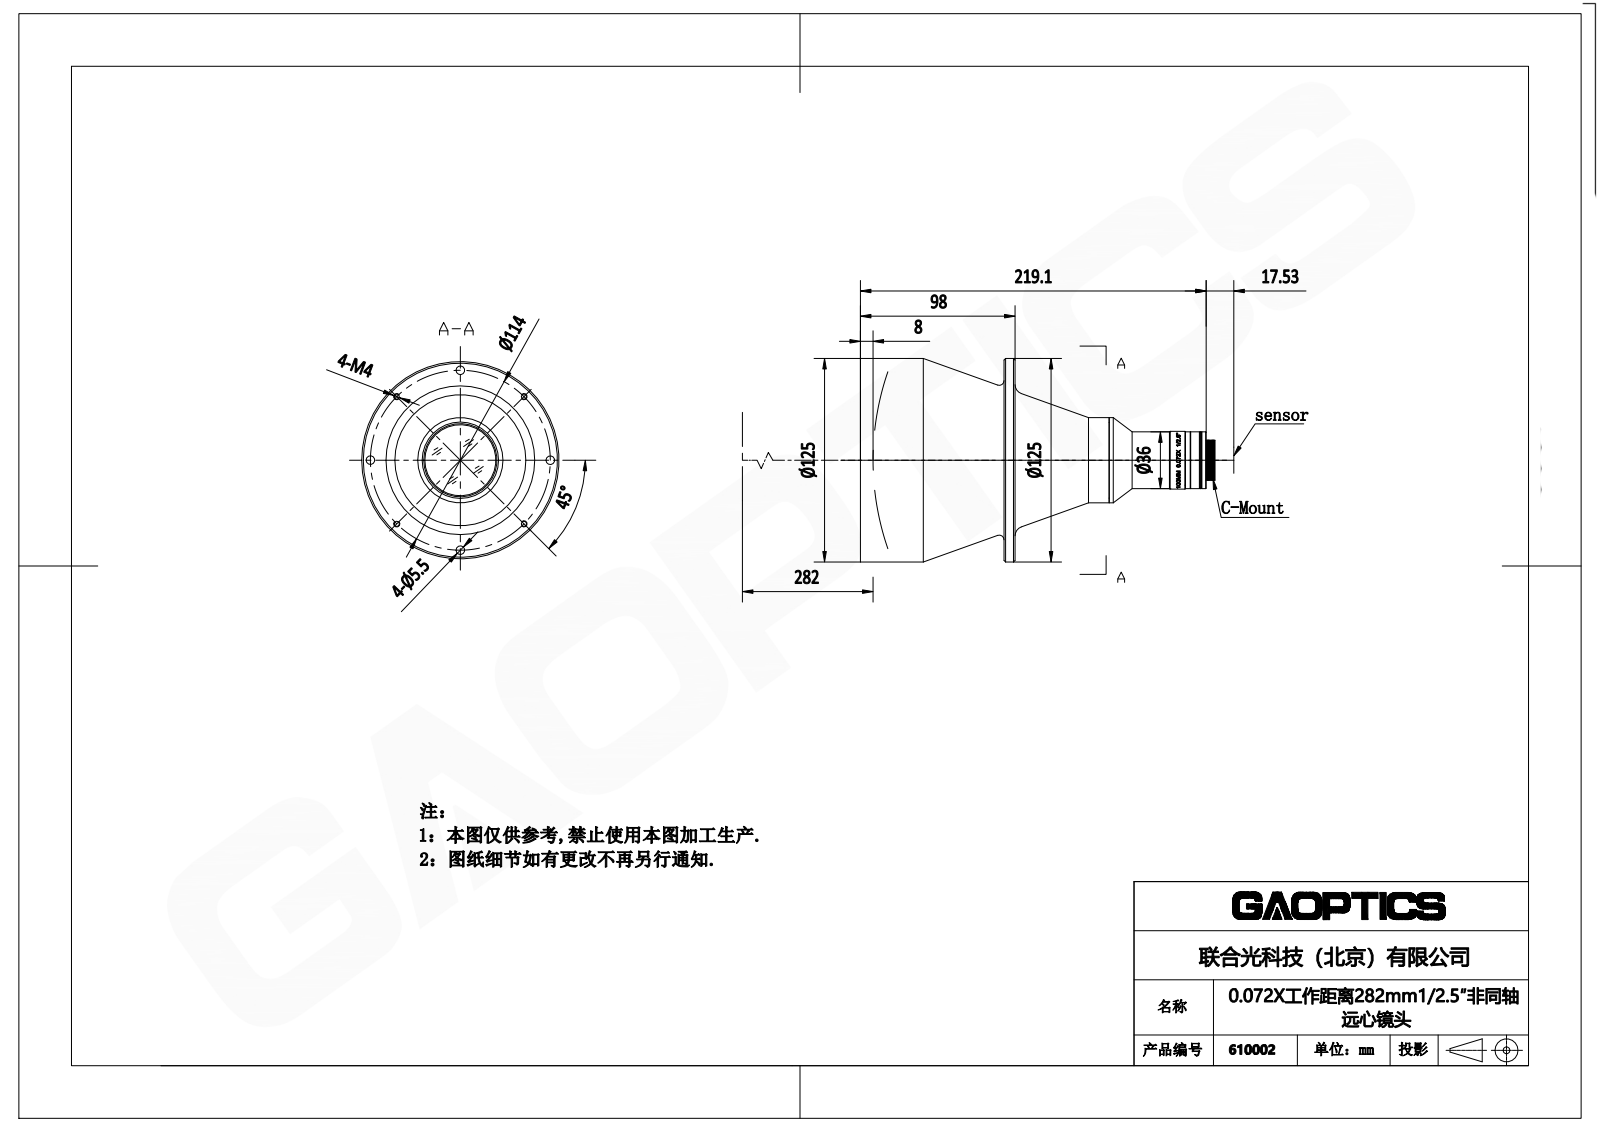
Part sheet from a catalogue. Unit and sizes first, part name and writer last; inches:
Units: inches
Overall size (bounding box): 8.839 × 4.974 × 4.921
Round holes (diameter × count): ⌀0.157 ×4, ⌀0.217 ×4, ⌀0.087 ×3, ⌀0.118 ×3, ⌀0.45 ×1, ⌀0.661 ×1, ⌀0.701 ×1, ⌀0.862 ×1, ⌀0.969 ×1, ⌀1.016 ×1, ⌀1.299 ×1, ⌀1.378 ×1
Round bosses / shafts (diameter × count): ⌀4.921 ×1, ⌀4.685 ×1, ⌀2.126 ×1, ⌀1.441 ×1, ⌀1.417 ×1, ⌀1.244 ×1, ⌀1 ×1, ⌀0.966 ×1
Partial cylindrical surfaces — rounded edges, fillets, slot ends (radius × count): R0.02 ×2, R0.717 ×1, R0.953 ×1
Main face-to-face distances: 3.177, 3.169, 2.902, 2.894, 0.276, 0.369, 0.376, 3.27, 3.546, 0.354
Hole centre spacings: 1.778, 2.323, 3.285, 1.778, 4.292, 4.292, 0.571, 0.989
Bodies: 0 solids, 502 faces (102 planar, 144 cylindrical, 256 other)
Part name (STEP PRODUCT): 610002
STEP written by: SolidWorks 2020 (CONFIG_CONTROL_DESIGN)
